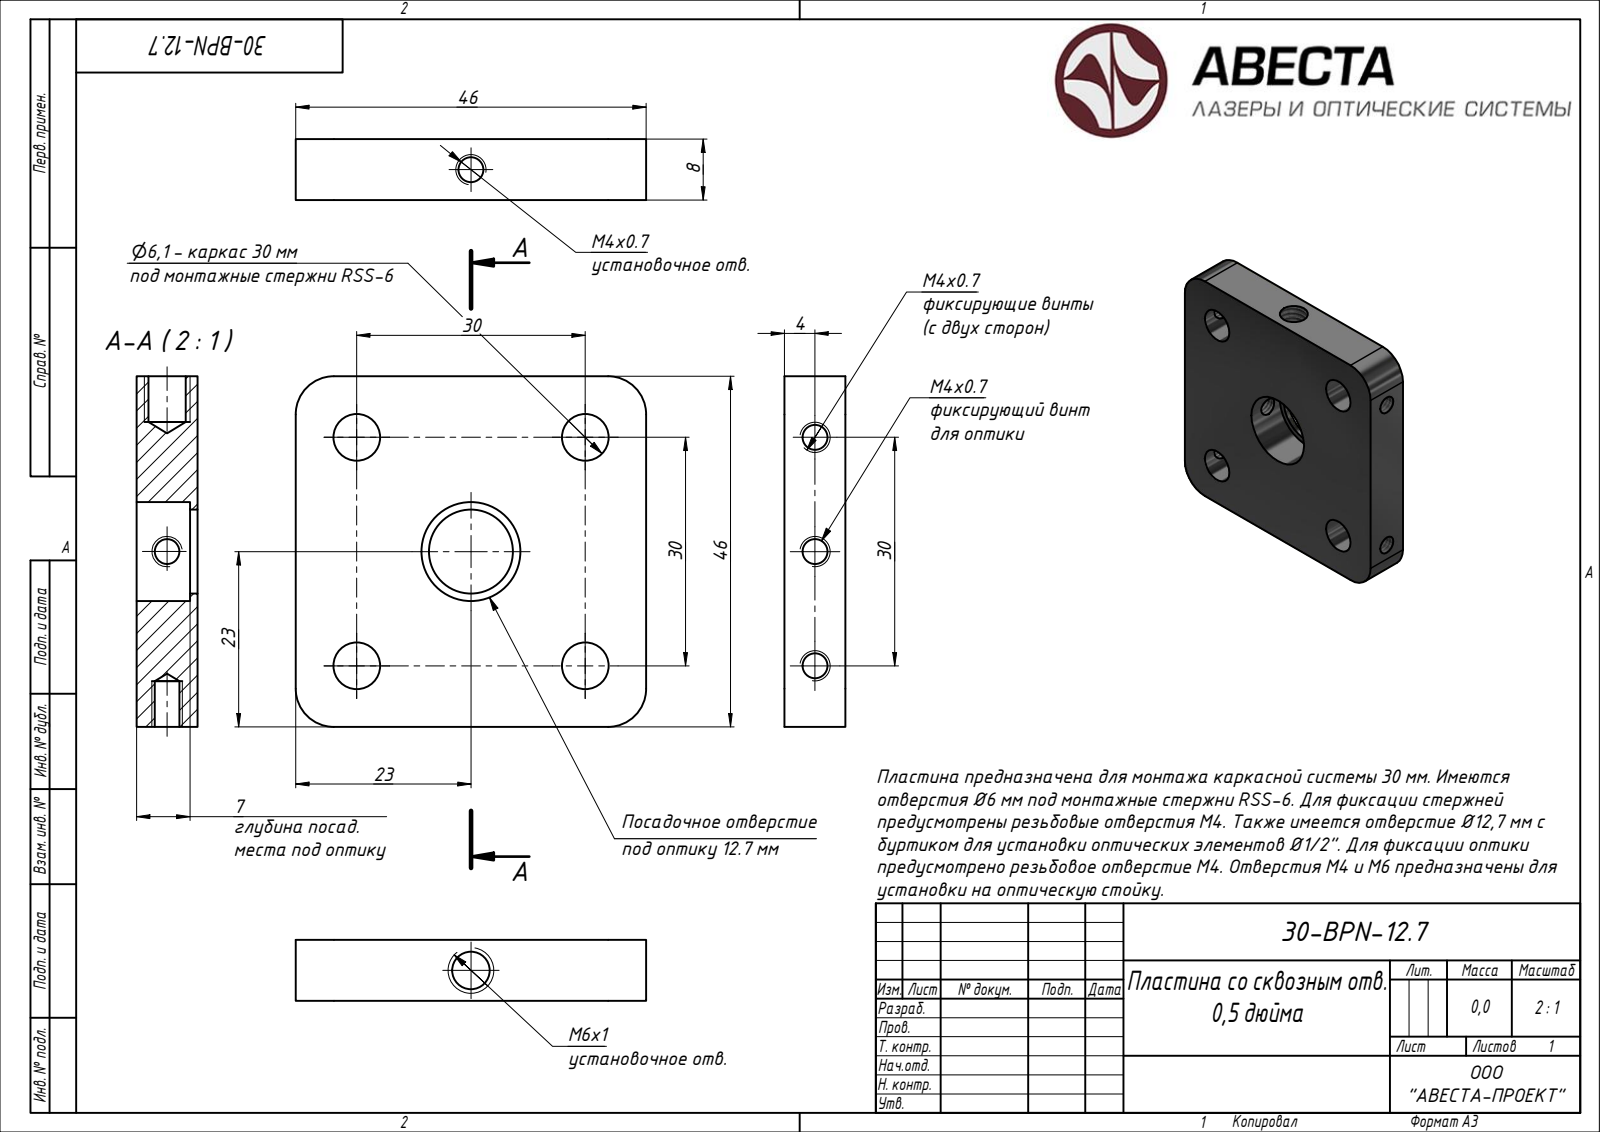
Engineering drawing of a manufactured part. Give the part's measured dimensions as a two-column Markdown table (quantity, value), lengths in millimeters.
| quantity | value |
| --- | --- |
| part name | 30-BPN-12.7 |
| STEP written by | Autodesk Inventor 2020 (AUTOMOTIVE_DESIGN) |
| units | millimeters |
| bodies | 1 solid, 26 faces (7 planar, 17 cylindrical, 2 other) |
| overall size | 46 × 46 × 8 |
| volume | 14 318 mm³ |
| surface area | 6 557 mm² |
| round holes (diameter × count) | 3.24 × 4, 6.1 × 4, 4.92 × 1, 11 × 1, 13 × 1 |
| partial cylindrical surfaces (radius × count) | 5 × 4 |
| main face-to-face distances | 8, 46, 1, 7 |
| hole center spacings | 30, 21.21, 15, 42.43 |
